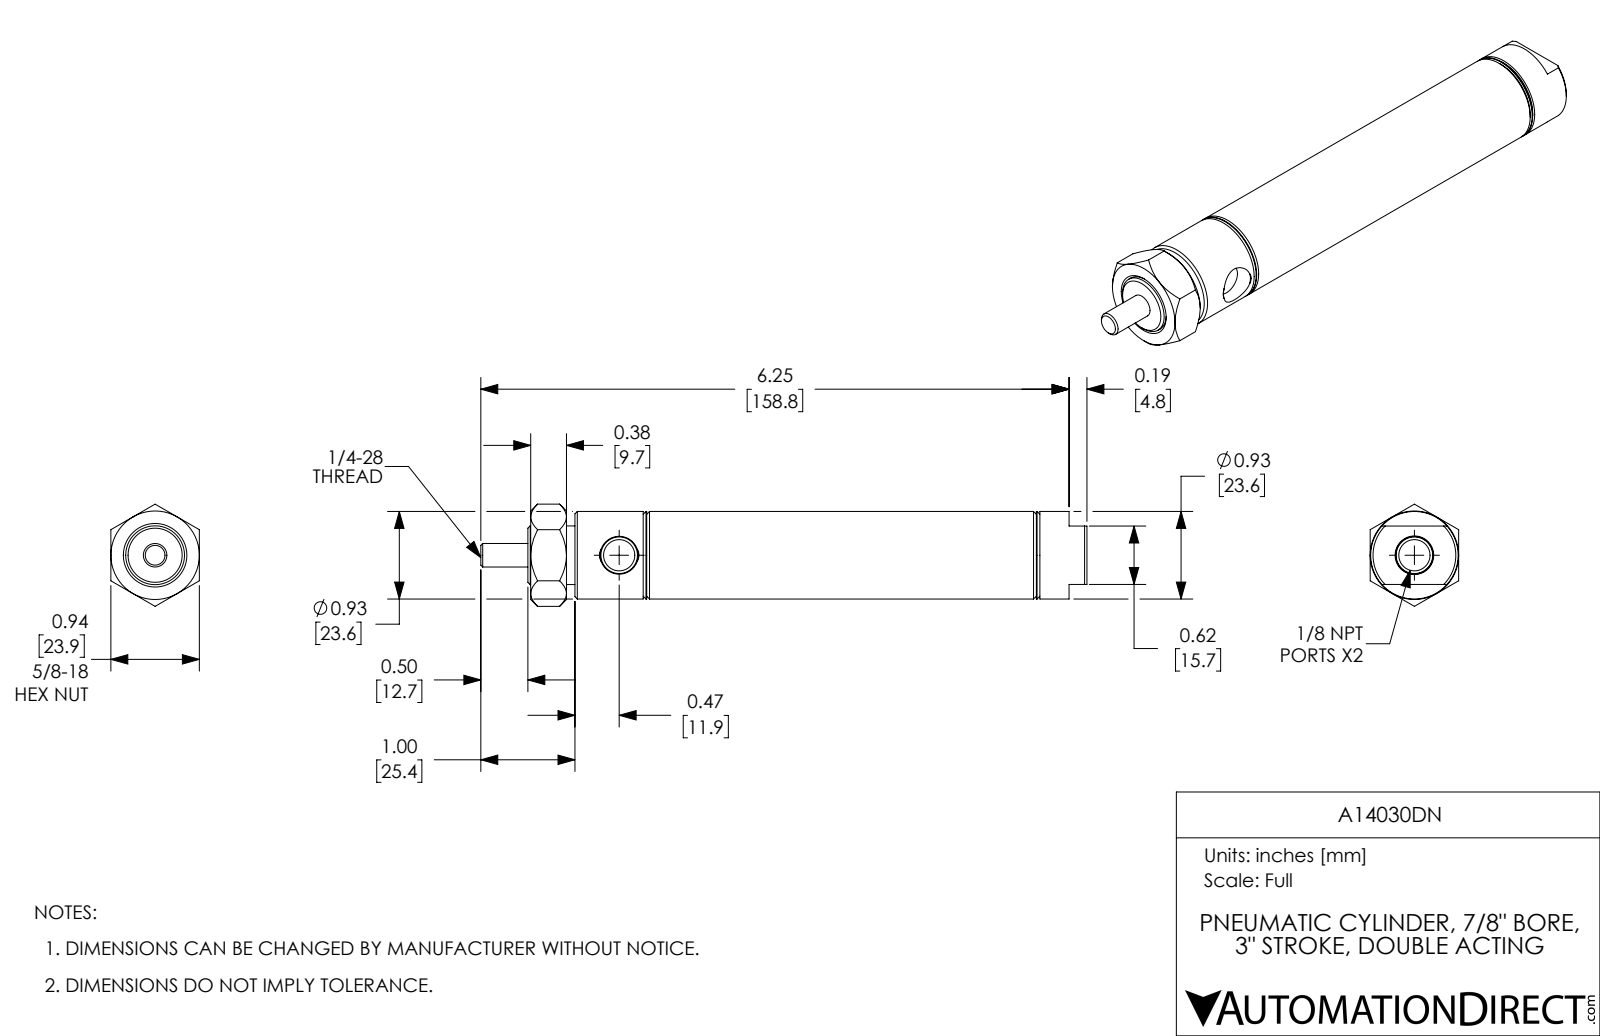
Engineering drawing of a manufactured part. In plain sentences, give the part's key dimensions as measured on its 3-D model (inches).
The part is named "A14030DN; A14030DN_Mounting Nut_D-9; A14030DN_Rod; A14030DN_Main Body". Its 3-D file was written by "SolidWorks 2017 (AUTOMOTIVE_DESIGN)". It is 3 solids with 104 faces: 28 planar, 30 cylindrical and 46 other. Overall it measures 6.44 by 1.085 by 0.94 inches. Its volume is 2.3 cubic inches and its surface area 40.58 square inches. Round holes: 1 of diameter 0.25, 1 of diameter 0.332, 1 of diameter 0.625, 1 of diameter 0.875. Round bosses or shafts: 1 of diameter 0.93, 1 of diameter 0.623, 1 of diameter 0.562, 1 of diameter 0.332. The main face-to-face distances are 0.5, 3.5, 3, 0.94, 4.583, 0.857, 4.673, 4.173, 1.173, 5.44.
